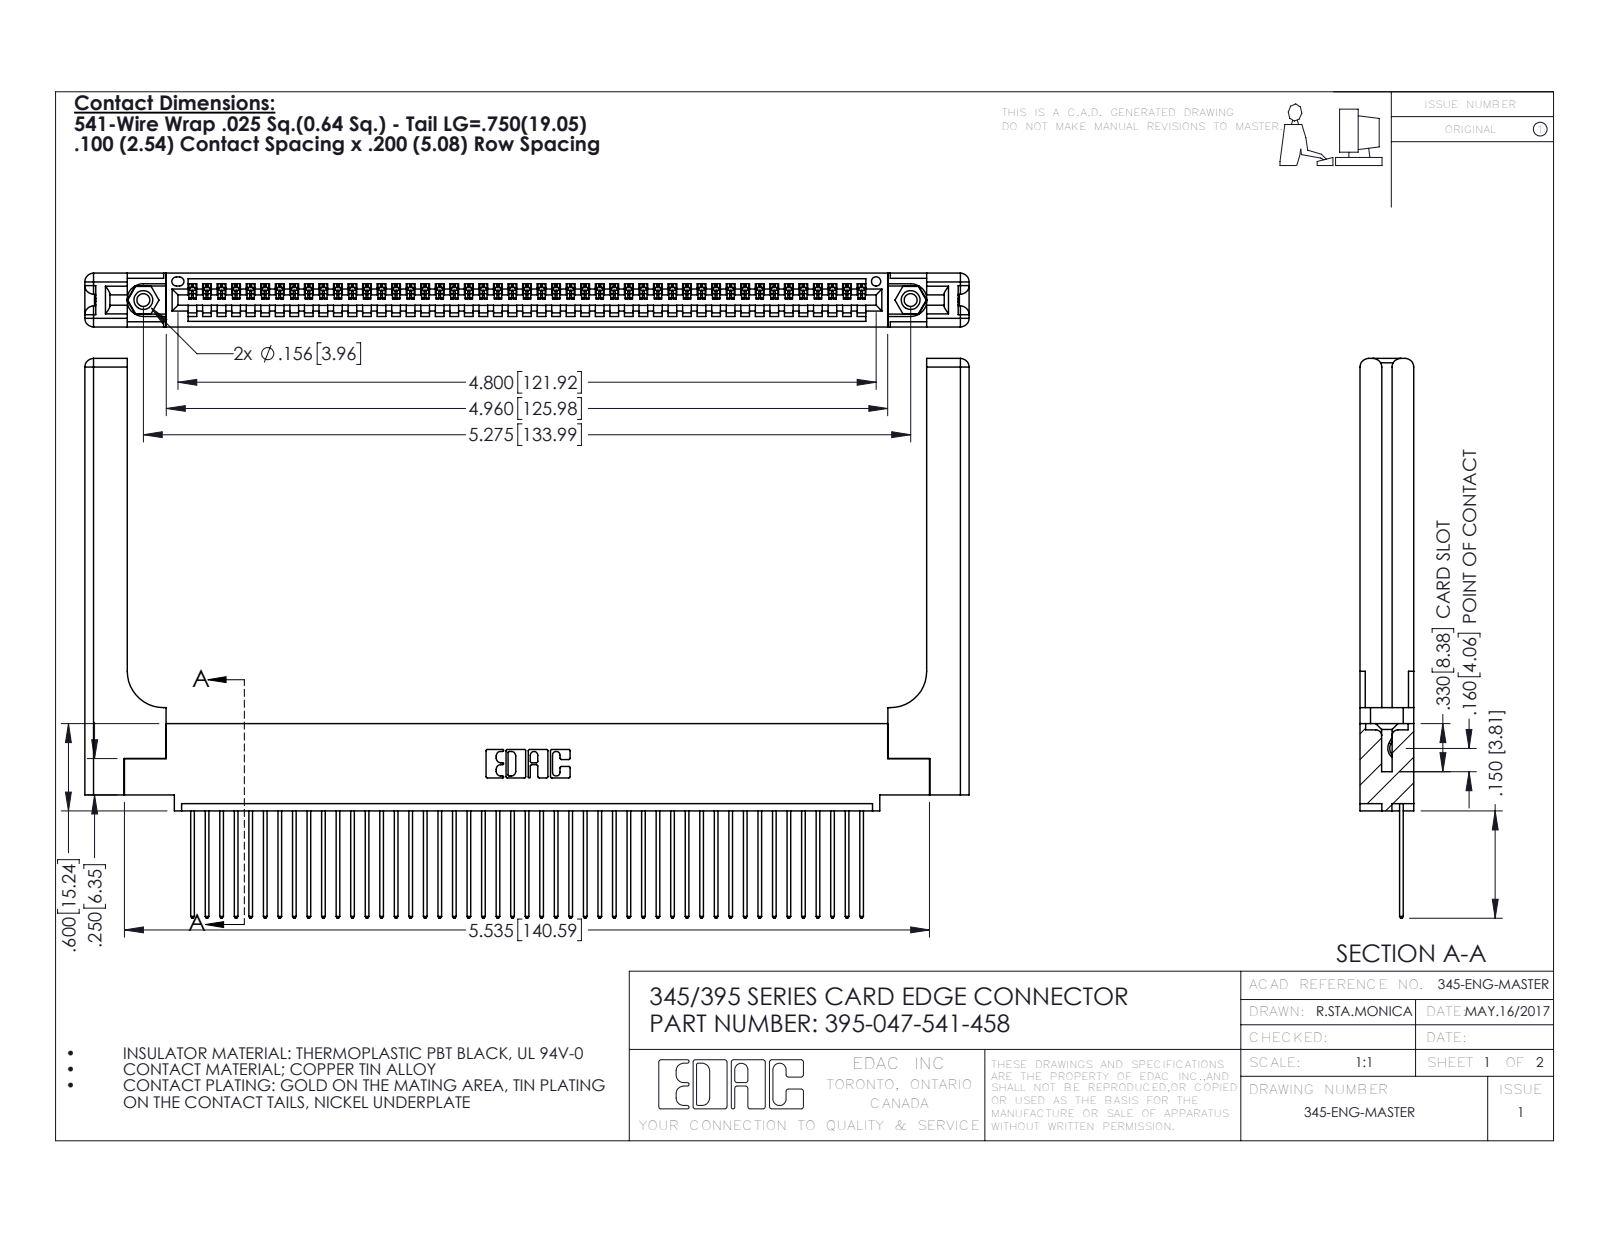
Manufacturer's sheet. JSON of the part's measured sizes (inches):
{"part_name": "345-250-001_345-250-001-102; 345-292-001_345-293-141; 395-047-541-458; 345-220-058_345-220-058 (+1 more)", "step_written_by": "SolidWorks 2016 (CONFIG_CONTROL_DESIGN)", "units": "inches", "bodies": {"solids": 52, "faces": 3112, "planar": 2112, "cylindrical": 940, "other": 60}, "overall_size": [6.079, 3.847, 0.37], "volume_in3": 1.421, "surface_area_in2": 40.33, "round_holes": [[0.089, 2], [0.125, 2], [0.156, 2], [0.064, 1]], "round_bosses_or_shafts": [[0.155, 2]], "partial_cylinders_radius": [[0.006, 94], [0.01, 94], [0.01, 22], [0.06, 16], [0.007, 6], [0.031, 6], [0.026, 3], [0.03, 2]], "face_to_face_distances": [0.072, 0.298, 0.37, 0.098, 0.272, 0.025, 0.2, 0.225, 0.148, 0.15], "hole_center_spacings": [0.27, 5.039, 5.275]}
